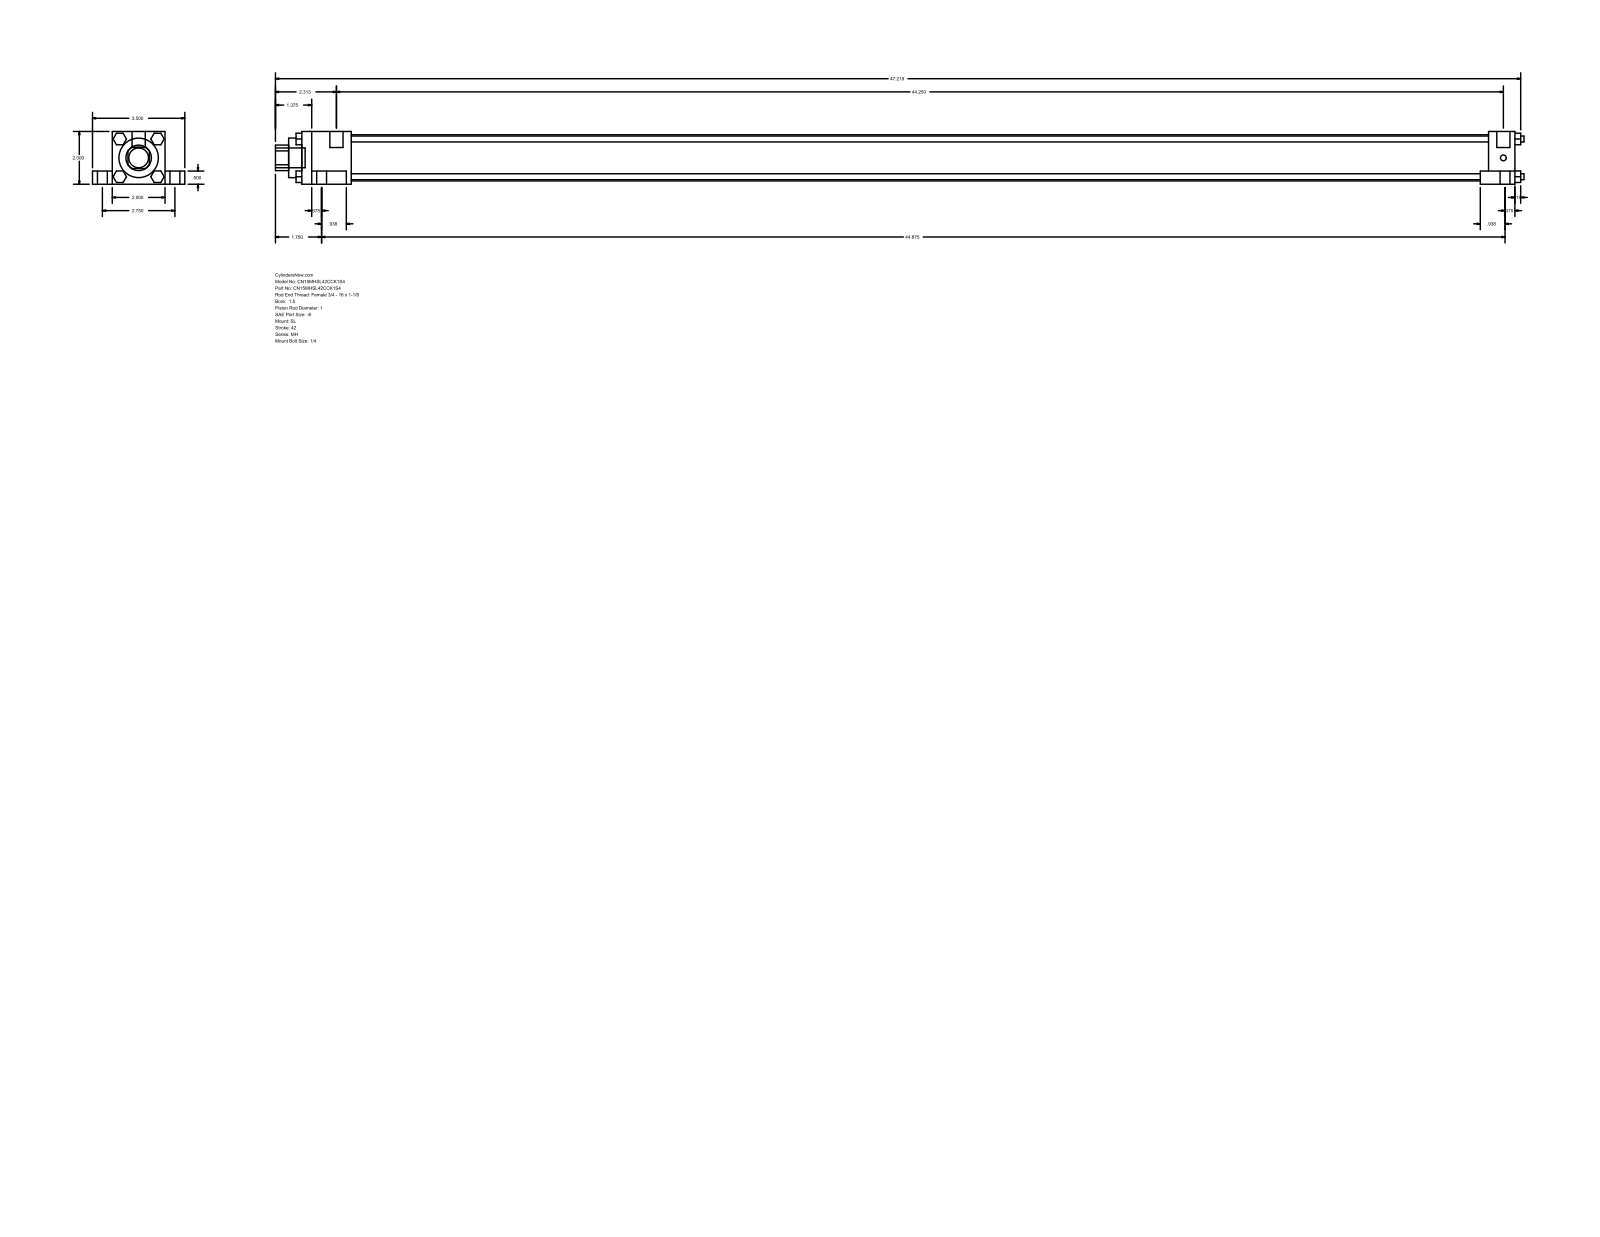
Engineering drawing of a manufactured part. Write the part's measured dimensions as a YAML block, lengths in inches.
part_name: "MH_SL__0150_1"
step_written_by: "GSSL Pune (CONFIG_CONTROL_DESIGN)"
units: inches
bodies: {solids: 0, faces: 148, planar: 112, cylindrical: 36, other: 0}
overall_size: [47.344, 3.5, 2]
round_holes:
  - {diameter: 1, count: 1}
  - {diameter: 1.5, count: 1}
  - {diameter: 1.75, count: 1}
round_bosses_or_shafts:
  - {diameter: 0.625, count: 4}
  - {diameter: 0.375, count: 4}
  - {diameter: 0.225, count: 4}
  - {diameter: 0.219, count: 4}
  - {diameter: 0.5, count: 2}
  - {diameter: 0.75, count: 1}
partial_cylinders:
  - {radius: 0.484, count: 1}
face_to_face_distances: [2, 0.5, 1.5, 0.75, 2.75, 46, 1, 0.375, 1.313, 44.313]
